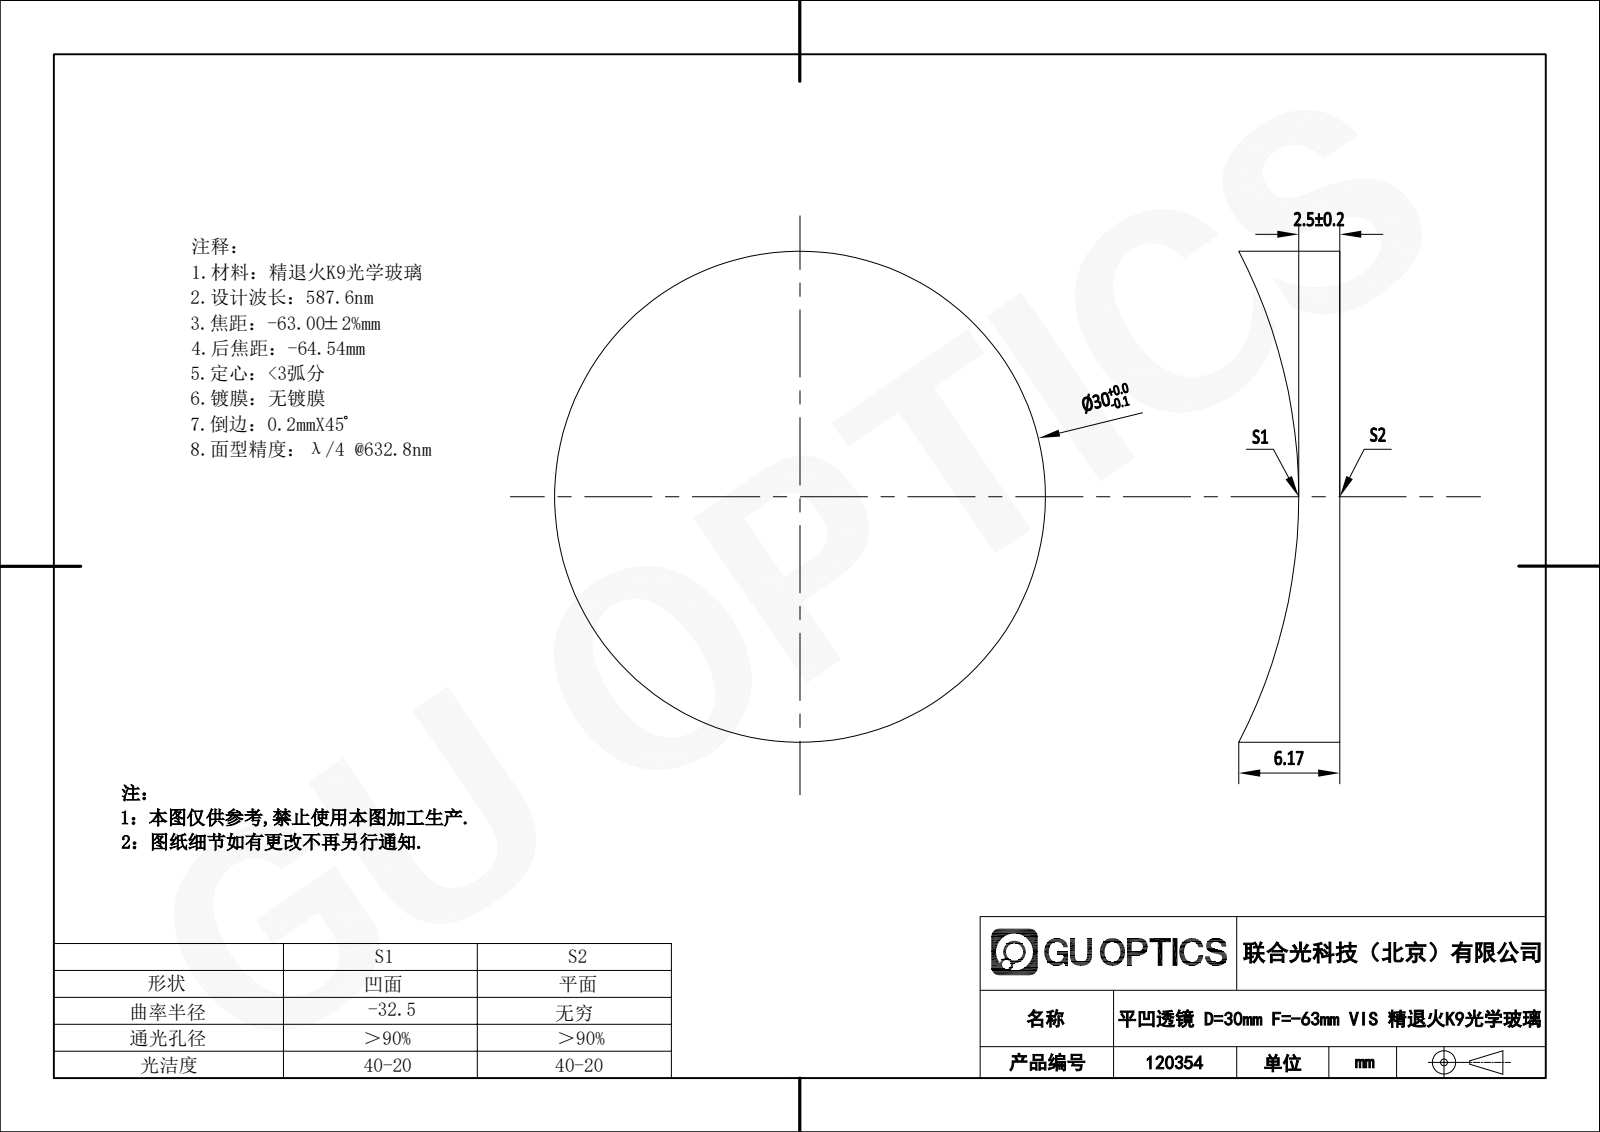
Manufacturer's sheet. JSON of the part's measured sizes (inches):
{"part_name": "120354", "step_written_by": "SolidWorks 2020 (CONFIG_CONTROL_DESIGN)", "units": "inches", "bodies": {"solids": 1, "faces": 5, "planar": 1, "cylindrical": 2, "other": 2}, "overall_size": [1.181, 1.181, 0.243], "volume_in3": 0.185, "surface_area_in2": 3.159, "round_bosses_or_shafts": [[1.181, 1]]}
